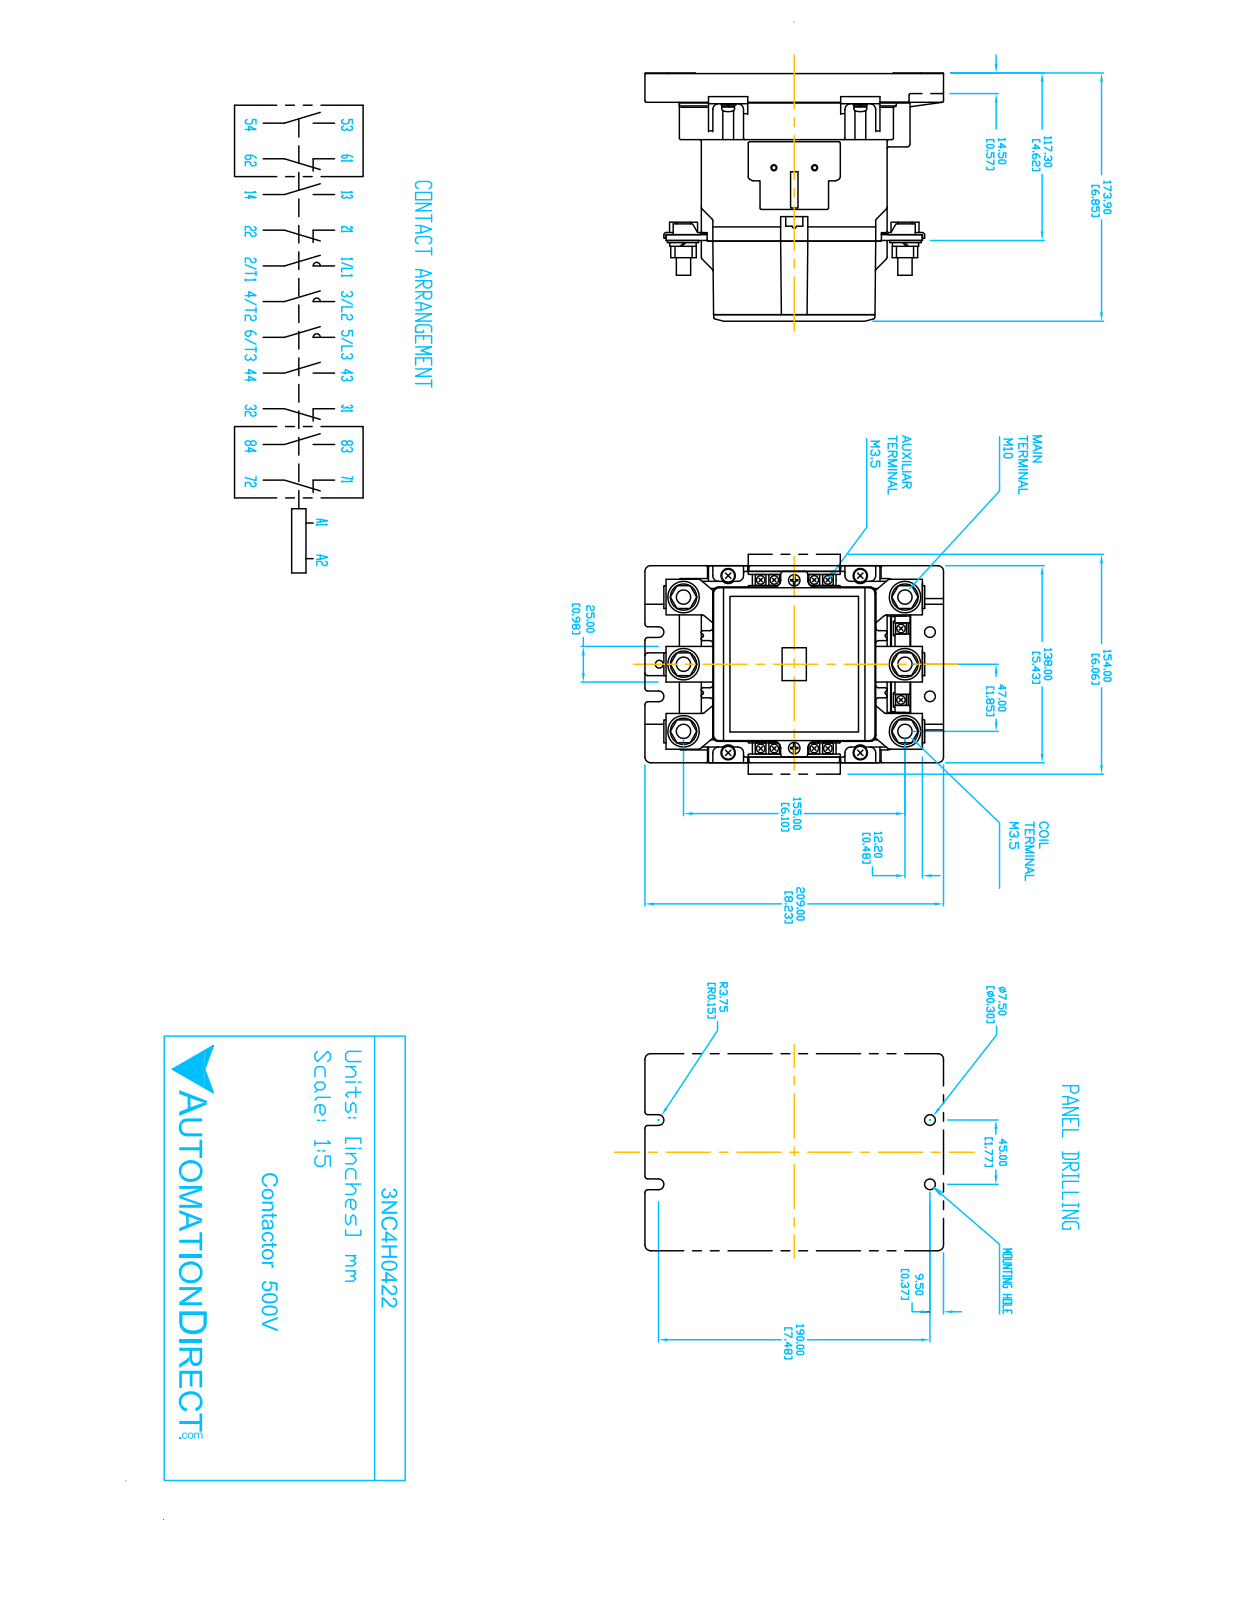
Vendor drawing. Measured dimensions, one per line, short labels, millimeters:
name: 3NC4H0422
written by: SolidWorks 2018 (AUTOMOTIVE_DESIGN)
unit: mm
bodies: 20 solids, 376 faces (258 planar, 118 cylindrical, 0 other)
size: 209 × 176 × 138
volume: 2 943 000 mm³; area: 211 000 mm²
holes: 8× ⌀8, 6× ⌀10, 2× ⌀7.5
rounds: 22× R2, 16× R4, 8× R0.8, 8× R1, 4× R5, 4× R5.5, 2× R0.5, 2× R3.8
face distances: 119.9, 123, 15, 120.3, 0.4, 108, 176, 56.1, 55.7, 8
hole spacings: 47, 78.4, 97.4, 131.3, 162, 155, 28.5, 30.1
